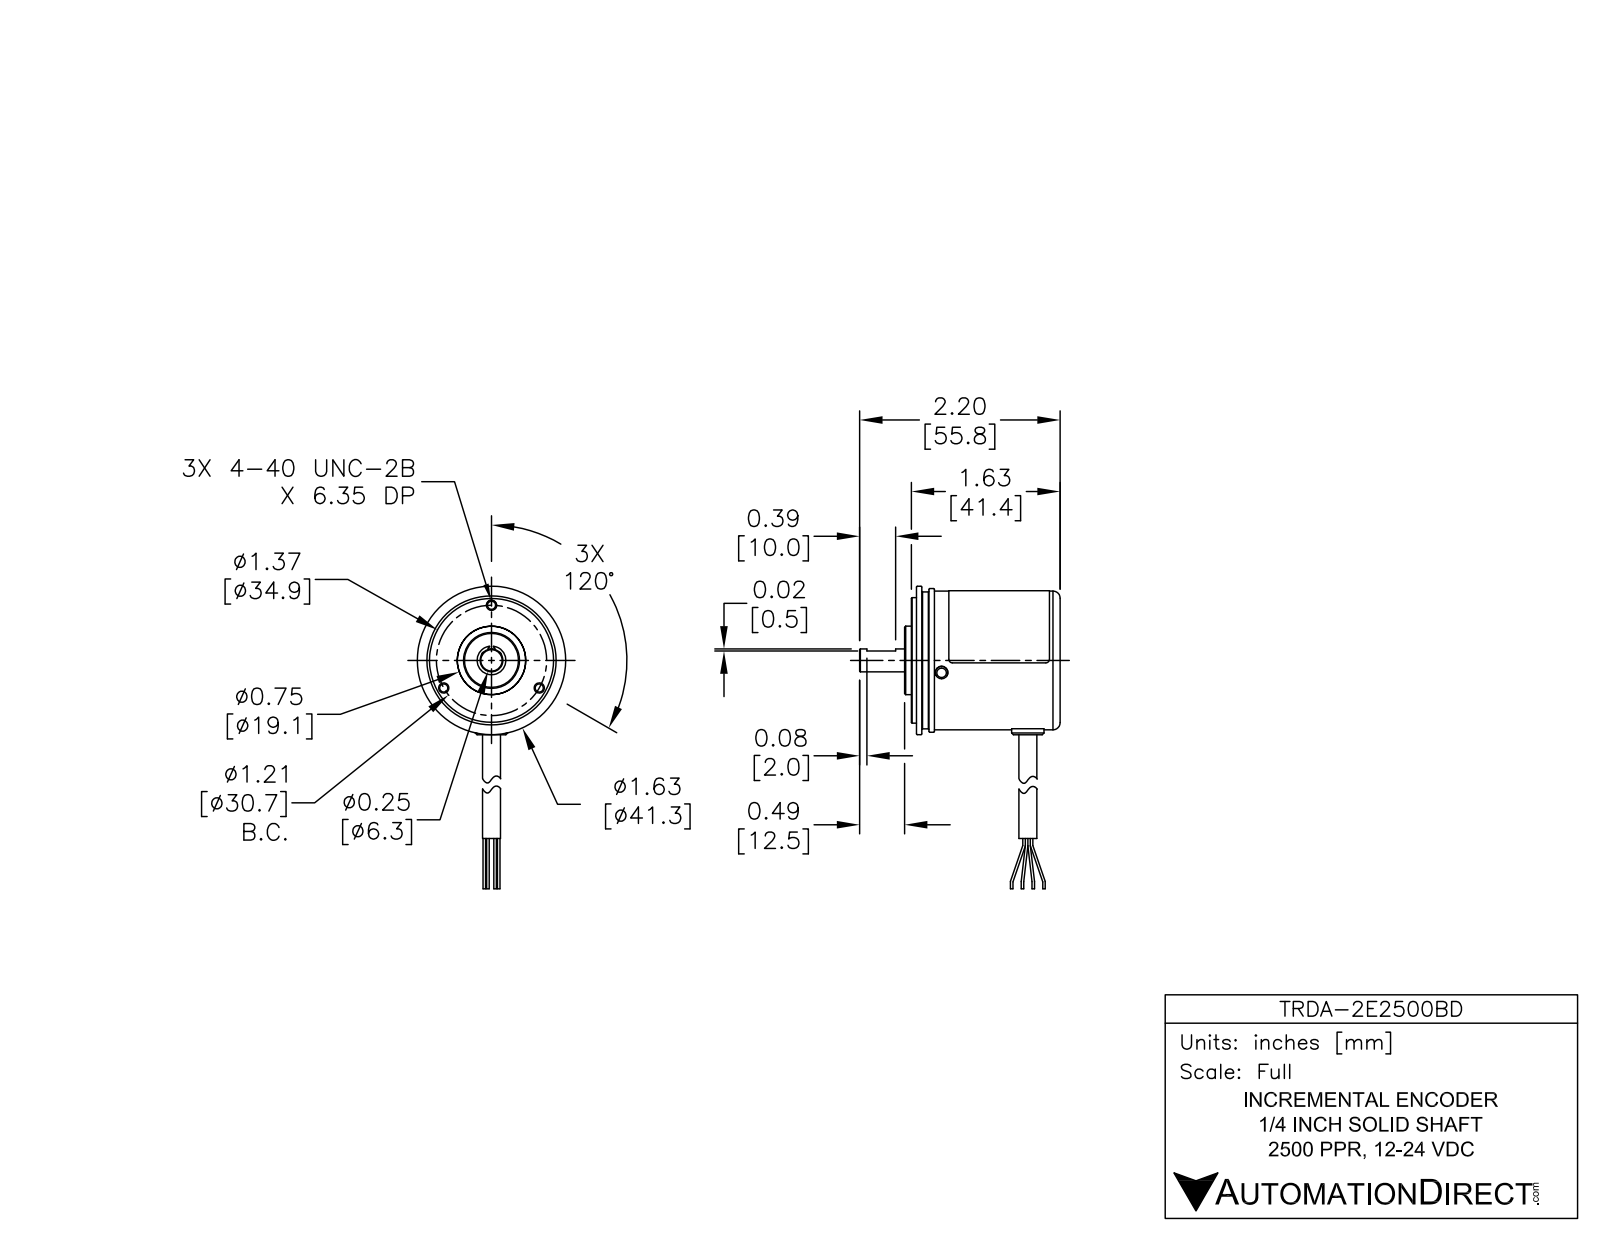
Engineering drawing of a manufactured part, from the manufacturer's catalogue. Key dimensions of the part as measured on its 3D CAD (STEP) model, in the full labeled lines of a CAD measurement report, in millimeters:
Part name (STEP PRODUCT): TRDA-2E1000BD
STEP written by: SolidWorks 2017 (AUTOMOTIVE_DESIGN)
Units: millimetres
Bodies: 3 solids, 146 faces (38 planar, 51 cylindrical, 57 other)
Overall size (bounding box): 149.9 × 69 × 41.3
Volume: 52 260 mm³ · Surface area: 10 920 mm²
Round holes (diameter × count): ⌀2.3 ×3, ⌀2.2 ×2, ⌀15 ×1
Round bosses / shafts (diameter × count): ⌀5 ×2, ⌀41.3 ×1, ⌀40 ×1, ⌀38.6 ×1, ⌀38.1 ×1, ⌀34.9 ×1, ⌀19.1 ×1, ⌀9 ×1
Partial cylindrical surfaces — rounded edges, fillets, slot ends (radius × count): R0.1 ×4, R0.2 ×2, R0.5 ×2, R3.3 ×2, R2.8 ×1, R18.7 ×1
Main face-to-face distances: 41.4, 1.4, 40, 1.5, 3.5, 2.9, 38.5, 2.8, 4.3, 42.8
Hole centre spacings: 26.6, 15.3, 15.3
